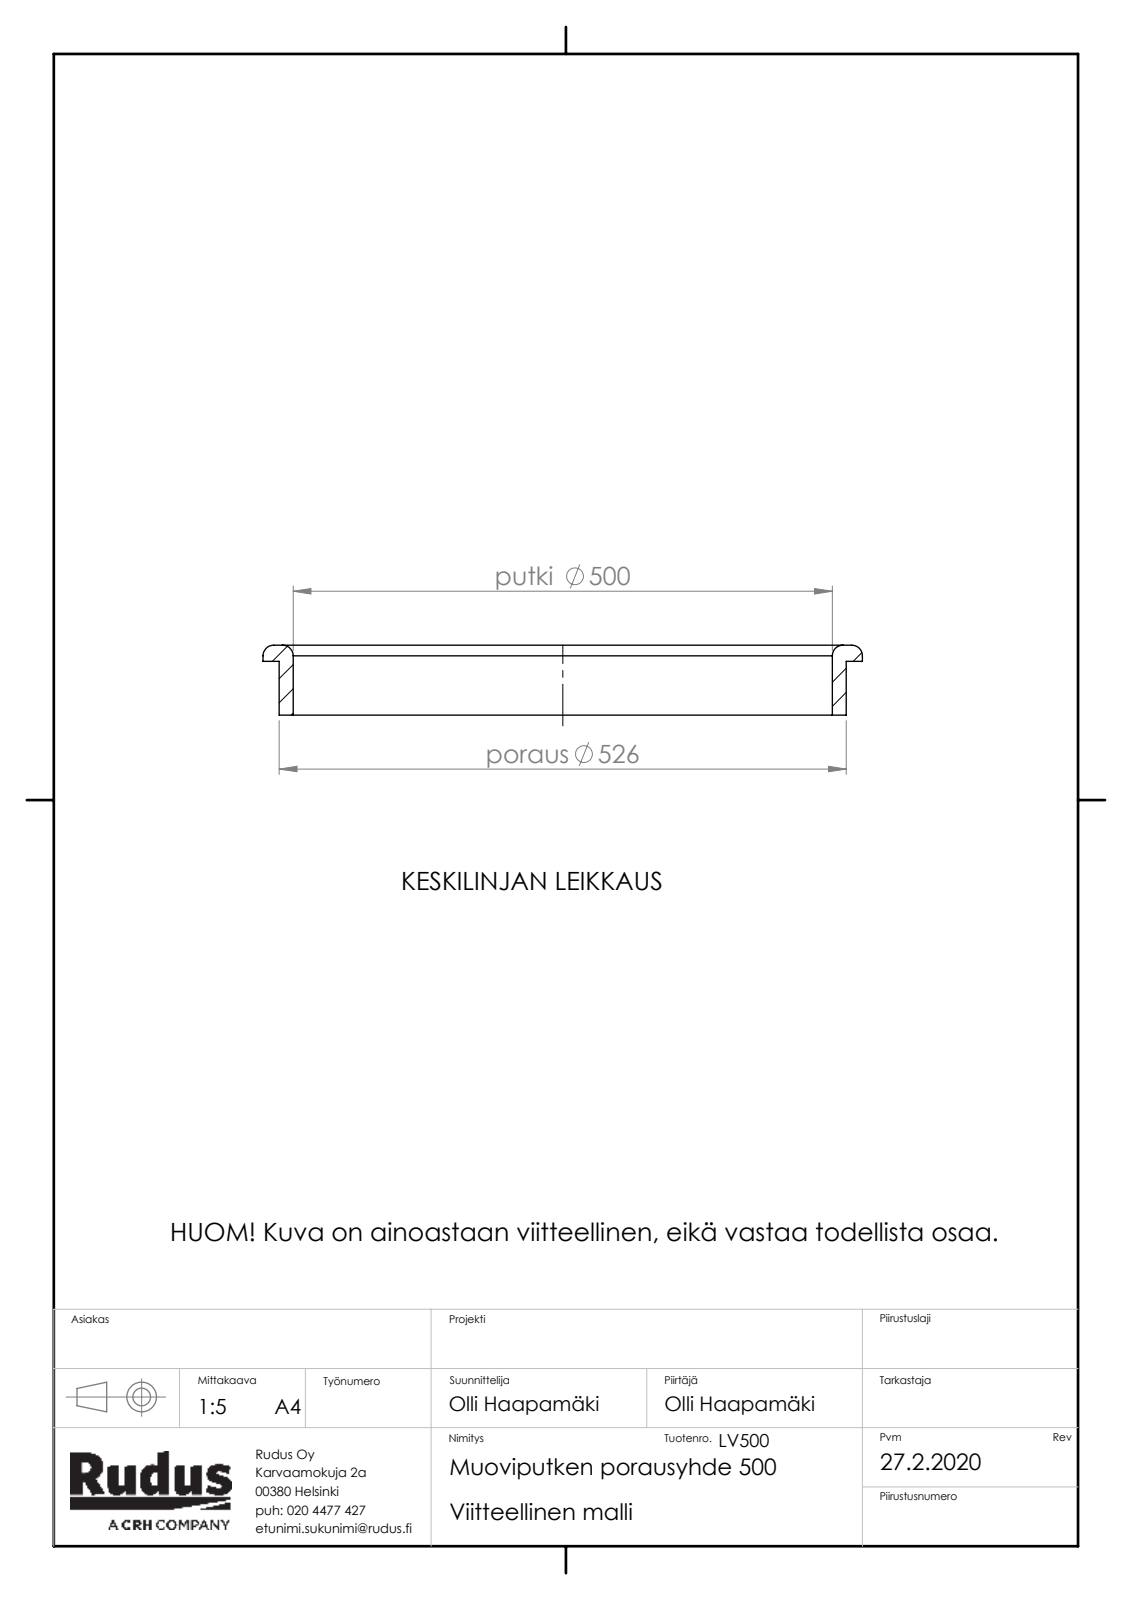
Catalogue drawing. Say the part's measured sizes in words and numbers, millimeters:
The part is named "kaivo-muovi-lapivienti; Rudus LV500 Muoviputken porausyhde 500". Its 3-D file was written by "SolidWorks 2019 (CONFIG_CONTROL_DESIGN)". It is 1 solid with 13 faces: 3 planar, 6 cylindrical and 4 other. Overall it measures 556 by 556 by 65 millimeters. Its volume is 1 673 000 cubic millimeters and its surface area 289 578 square millimeters. Round holes: 1 of diameter 500. Round bosses or shafts: 1 of diameter 556, 1 of diameter 526. The main face-to-face distances are 50, 65, 15.
